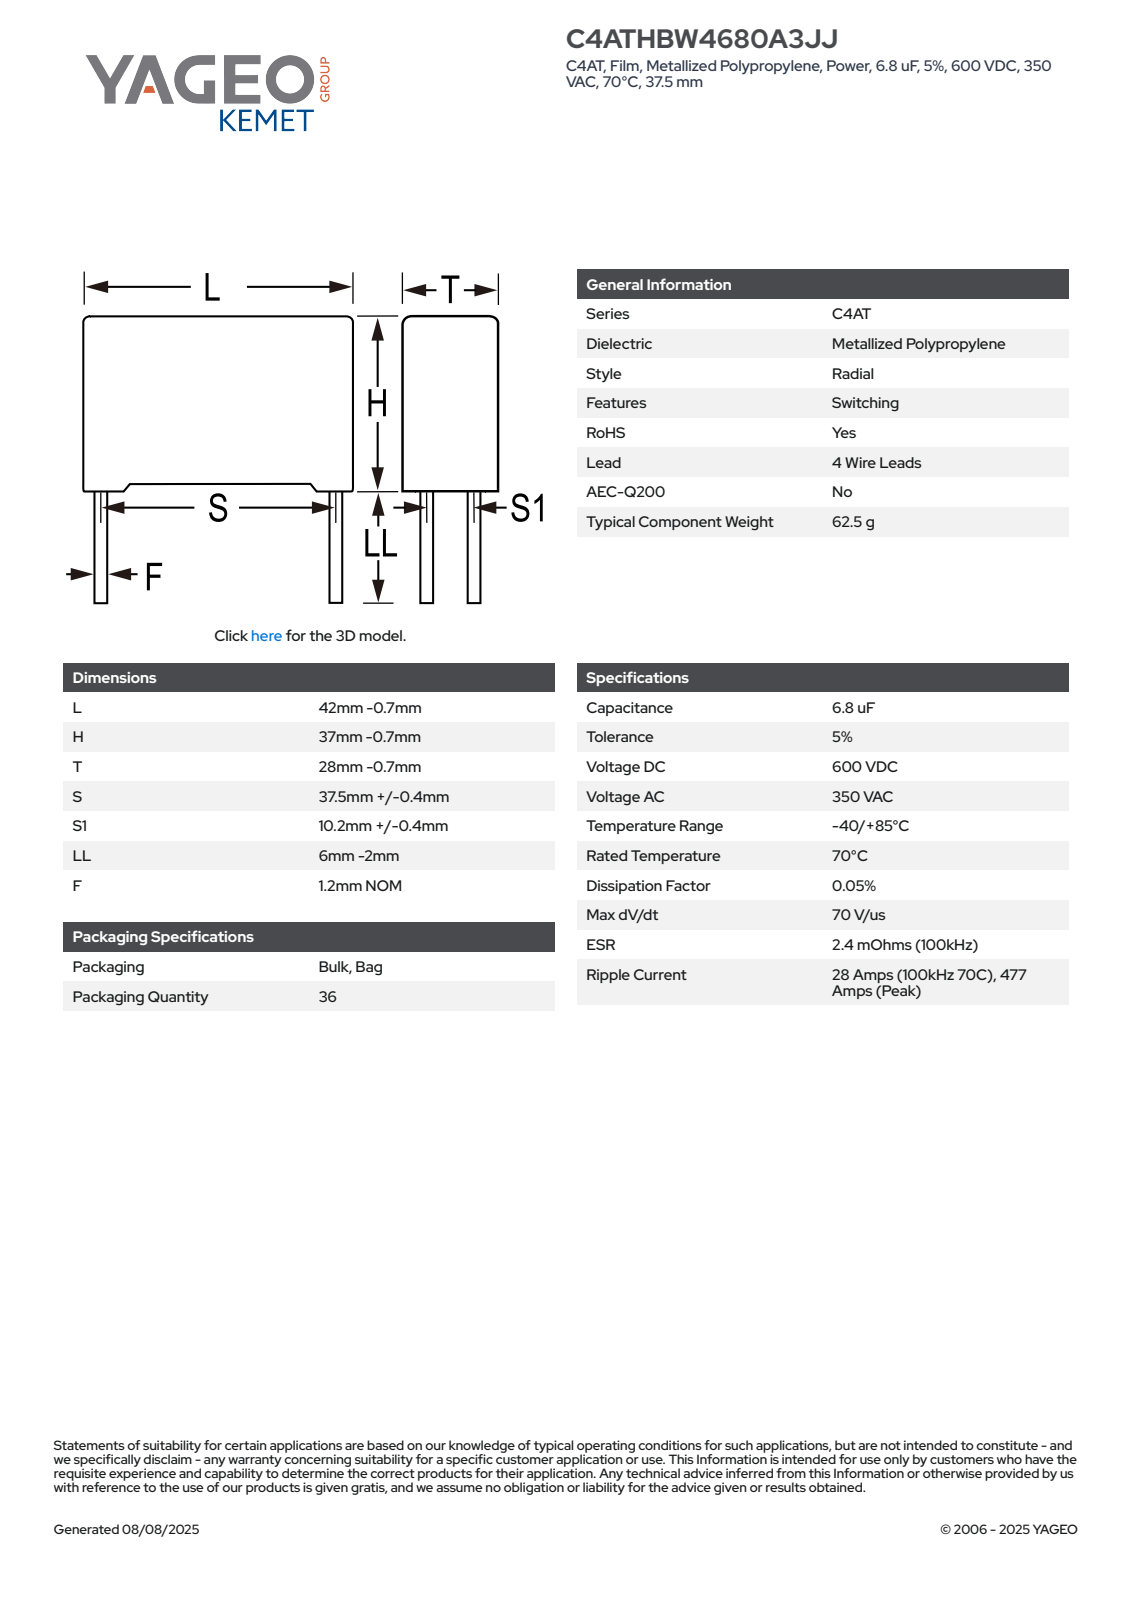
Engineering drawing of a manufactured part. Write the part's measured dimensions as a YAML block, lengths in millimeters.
part_name: "CFP_RB4_42X37X28_L41.3H36.3T27.3S37.5S110.2LL4F1.2"
step_written_by: "SolidWorks 2014 (AUTOMOTIVE_DESIGN)"
units: millimeters
bodies: {solids: 4, faces: 91, planar: 83, cylindrical: 8, other: 0}
overall_size: [41.3, 40.3, 27.3]
volume: 39881
surface_area: 7428
round_bosses_or_shafts:
  - {diameter: 1.2, count: 4}
face_to_face_distances: [27.3, 35.23, 41.3, 1.07, 36.3, 1.68, 27.31, 39.62, 37.94, 25.62]
